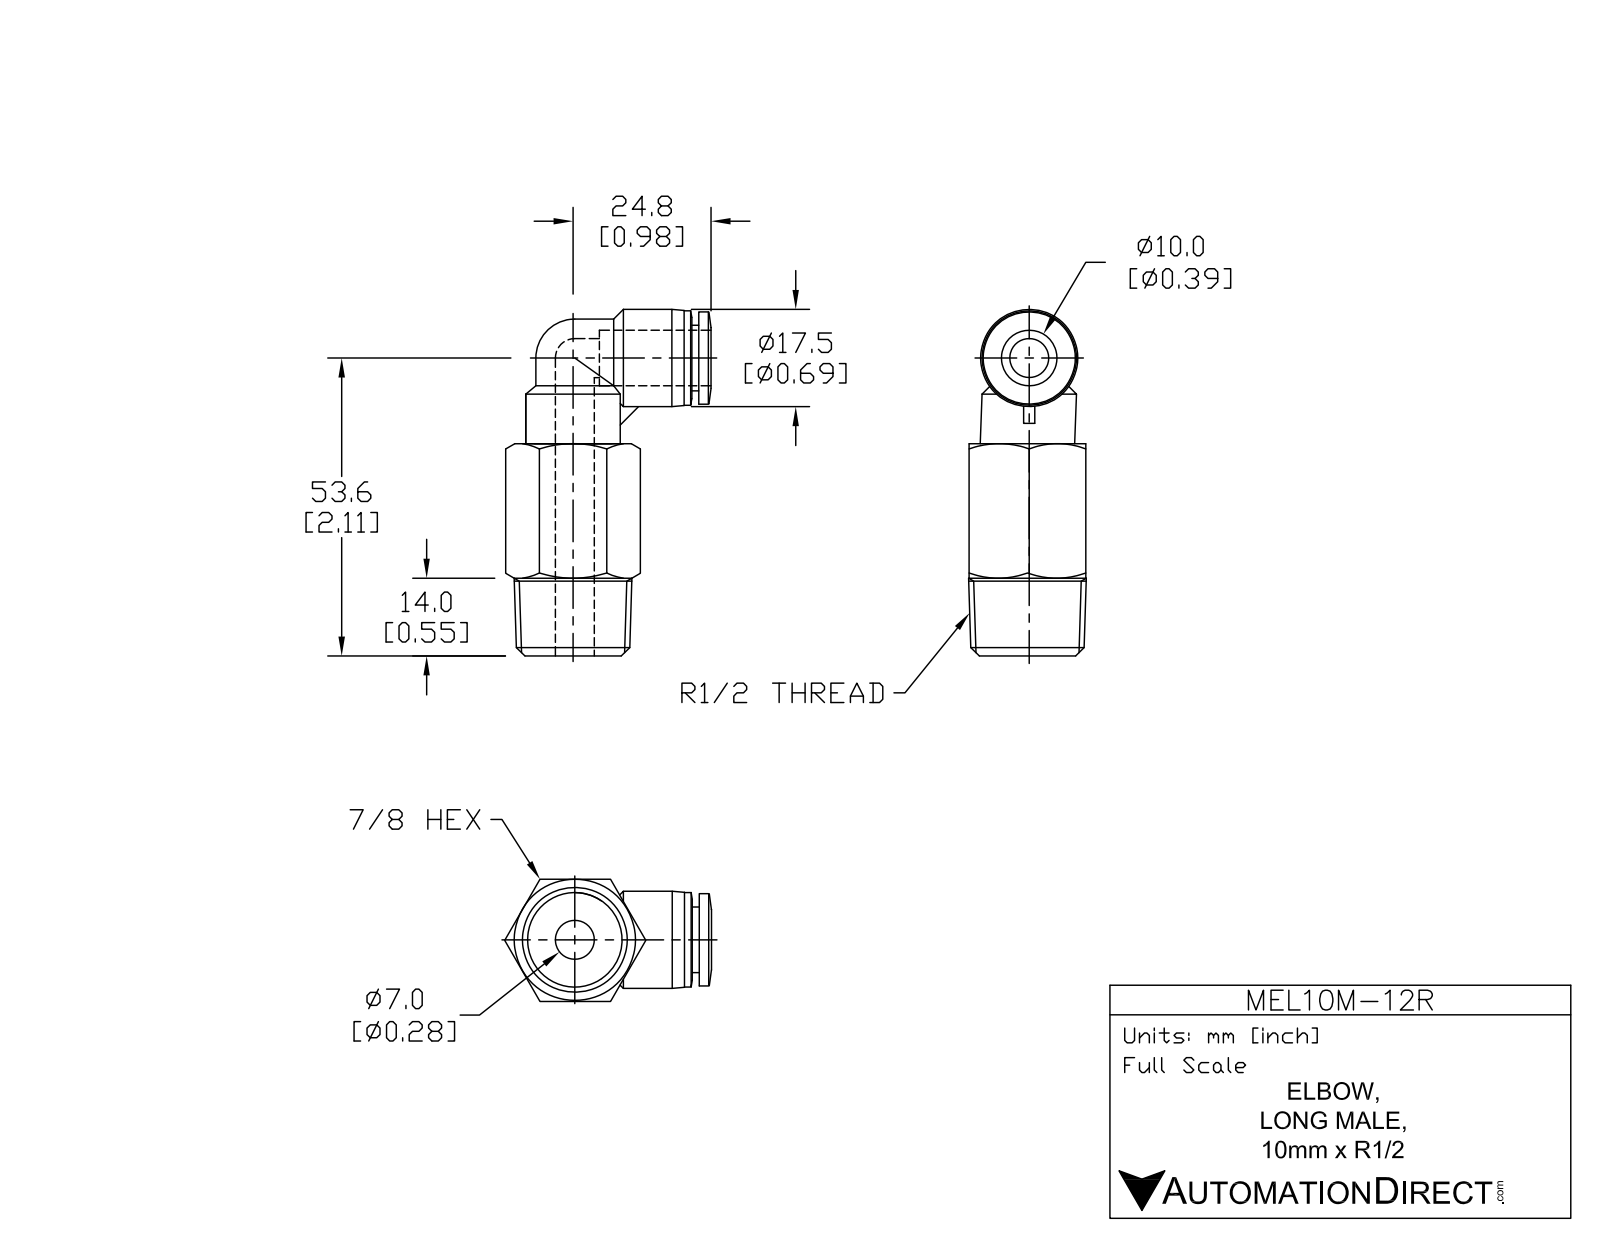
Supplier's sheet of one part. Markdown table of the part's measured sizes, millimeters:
| quantity | value |
| --- | --- |
| part name | MEL10M-12R |
| STEP written by | SolidWorks 2015 (AUTOMOTIVE_DESIGN) |
| units | millimeters |
| bodies | 1 solid, 70 faces (17 planar, 20 cylindrical, 33 other) |
| overall size | 62.5 × 37.3 × 22 |
| volume | 18 830 mm³ |
| surface area | 7 503 mm² |
| round holes (diameter × count) | 7 × 2, 10.3 × 1 |
| round bosses / shafts (diameter × count) | 17 × 2, 17.5 × 1, 16.6 × 1, 14 × 1, 11.8 × 1 |
| partial cylindrical surfaces (radius × count) | 7 × 1 |
| main face-to-face distances | 22, 38.2, 1.2, 16.7, 18, 14, 24.2, 10, 12, 2 |
